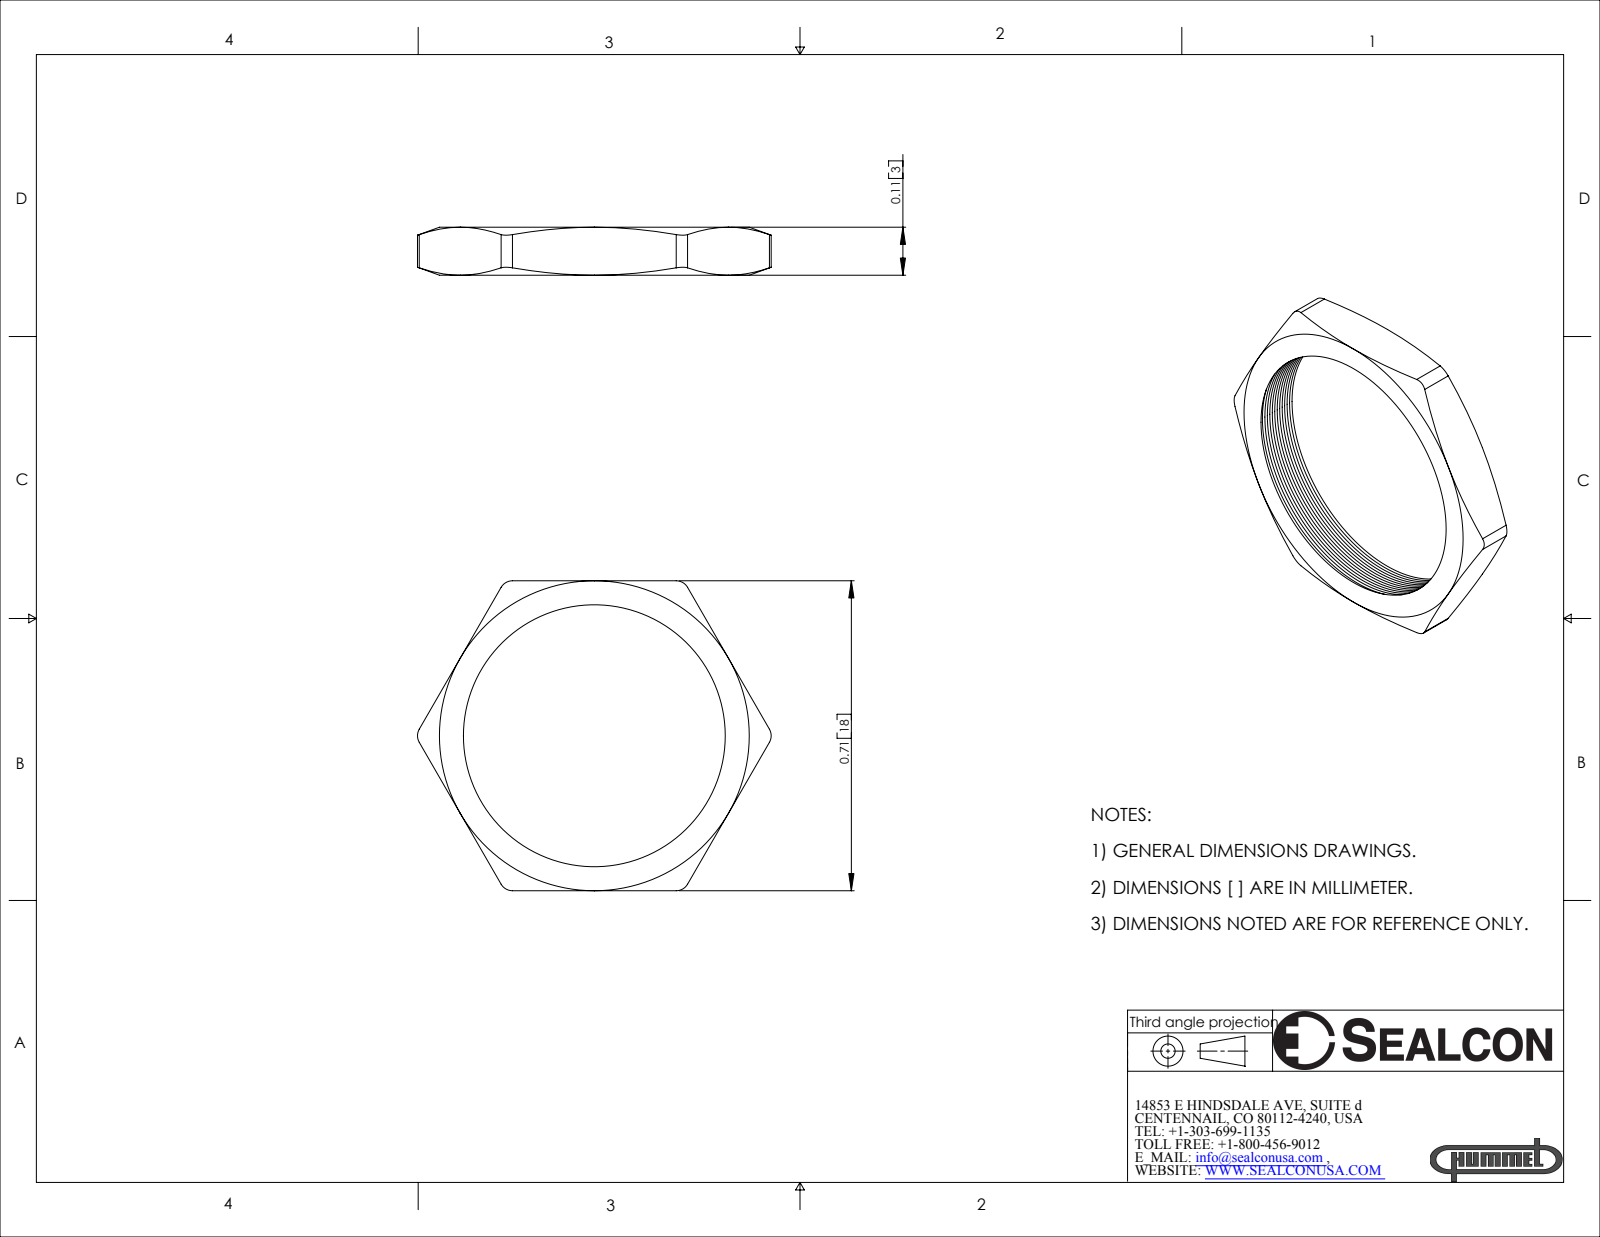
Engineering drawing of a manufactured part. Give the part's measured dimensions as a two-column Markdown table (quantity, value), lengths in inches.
| quantity | value |
| --- | --- |
| part name | NP-09-BR |
| STEP written by | SolidWorks 2007 (CONFIG_CONTROL_DESIGN) |
| units | inches |
| bodies | 1 solid, 83 faces (8 planar, 7 cylindrical, 68 other) |
| overall size | 0.811 × 0.71 × 0.11 |
| volume | 0.014 in³ |
| surface area | 0.958 in² |
| partial cylindrical surfaces (radius × count) | 0.03 × 6 |
| main face-to-face distances | 0.71, 0.11 |
